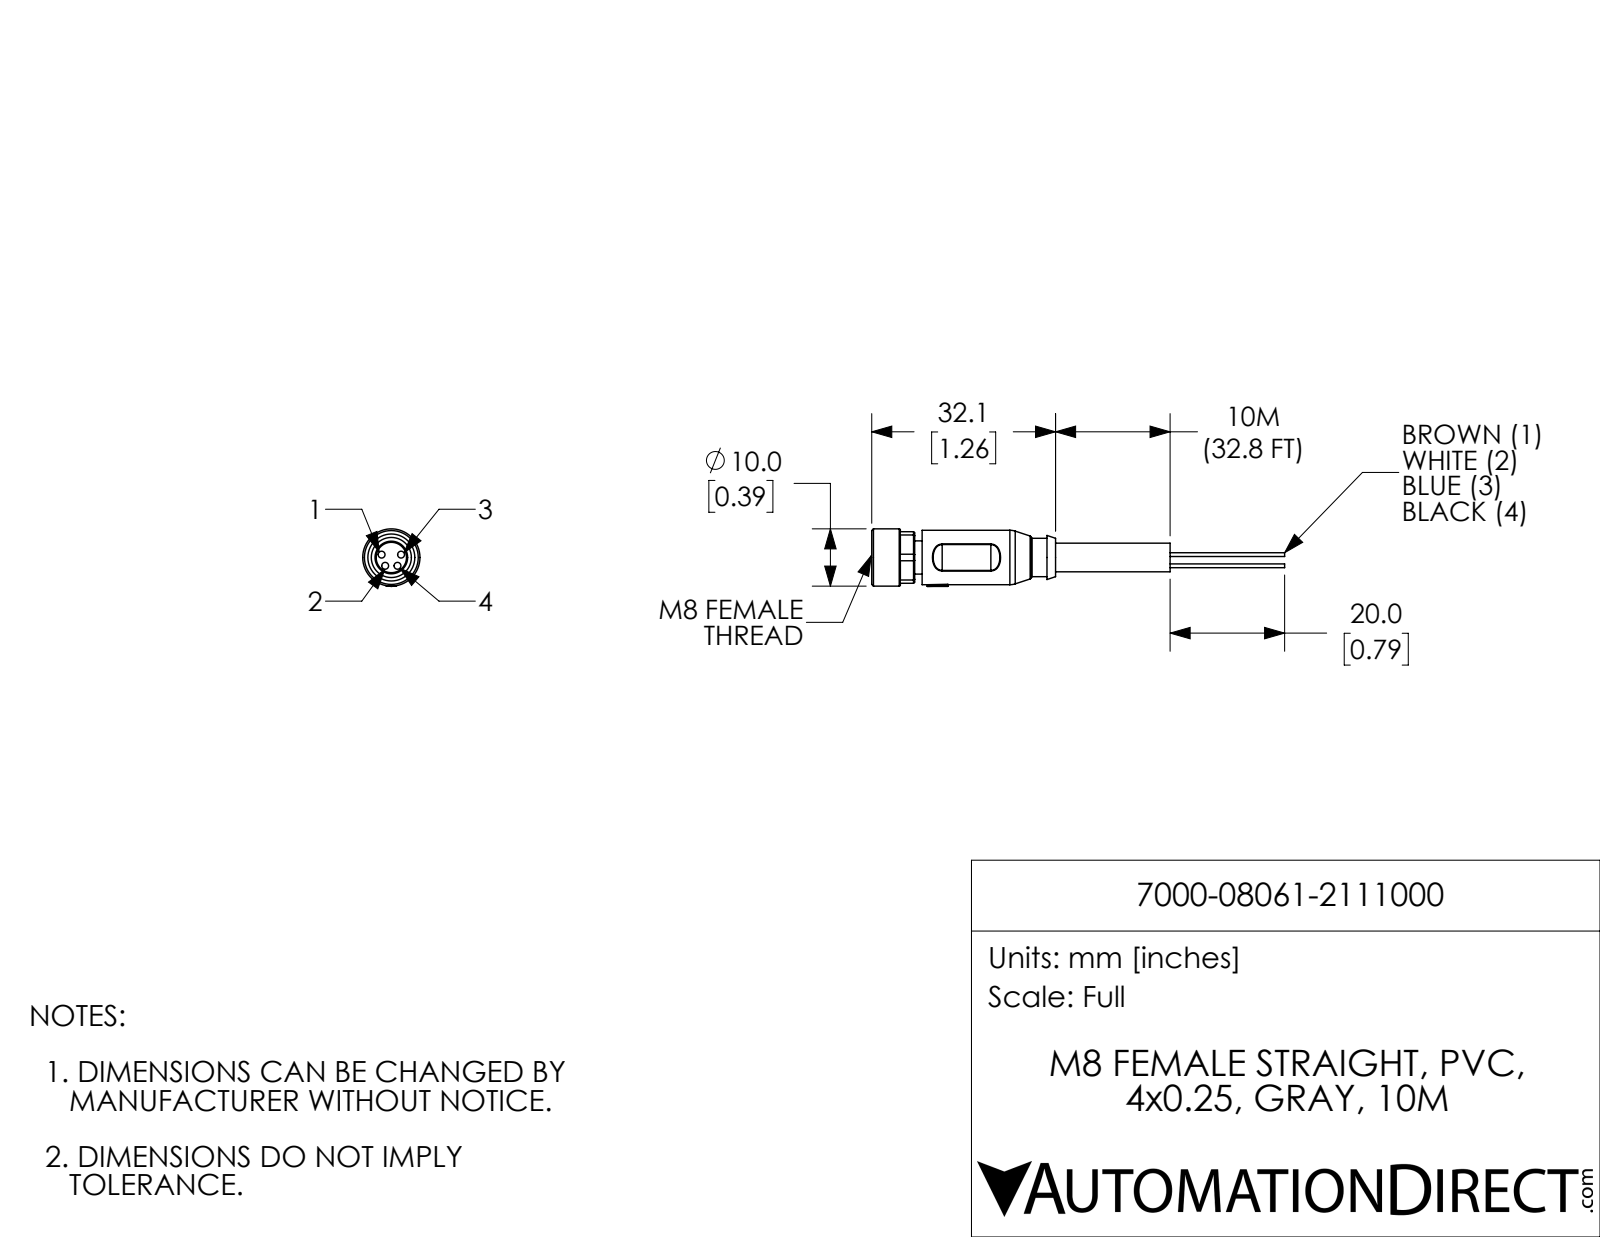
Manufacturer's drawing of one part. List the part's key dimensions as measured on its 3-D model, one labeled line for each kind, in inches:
Part name (STEP PRODUCT): 7000-08061-2111000
STEP written by: SolidWorks 2017 (AUTOMOTIVE_DESIGN)
Units: inches
Bodies: 1 solid, 115 faces (38 planar, 46 cylindrical, 31 other)
Overall size (bounding box): 2.839 × 0.396 × 0.394
Volume: 0.141 in³ · Surface area: 2.944 in²
Round holes (diameter × count): ⌀0.047 ×4, ⌀0.276 ×1
Round bosses / shafts (diameter × count): ⌀0.026 ×4, ⌀0.394 ×1, ⌀0.374 ×1, ⌀0.264 ×1, ⌀0.228 ×1, ⌀0.224 ×1, ⌀0.197 ×1
Partial cylindrical surfaces — rounded edges, fillets, slot ends (radius × count): R0.008 ×4, R0.098 ×4, R0.193 ×1, R0.199 ×1
Main face-to-face distances: 0.327, 0.051, 0.969, 0.354, 0.059, 0.028, 1.756, 1.705, 0.268, 0.319
Hole centre spacings: 0.07, 0.071, 0.081, 0.133, 0.084, 0.134
